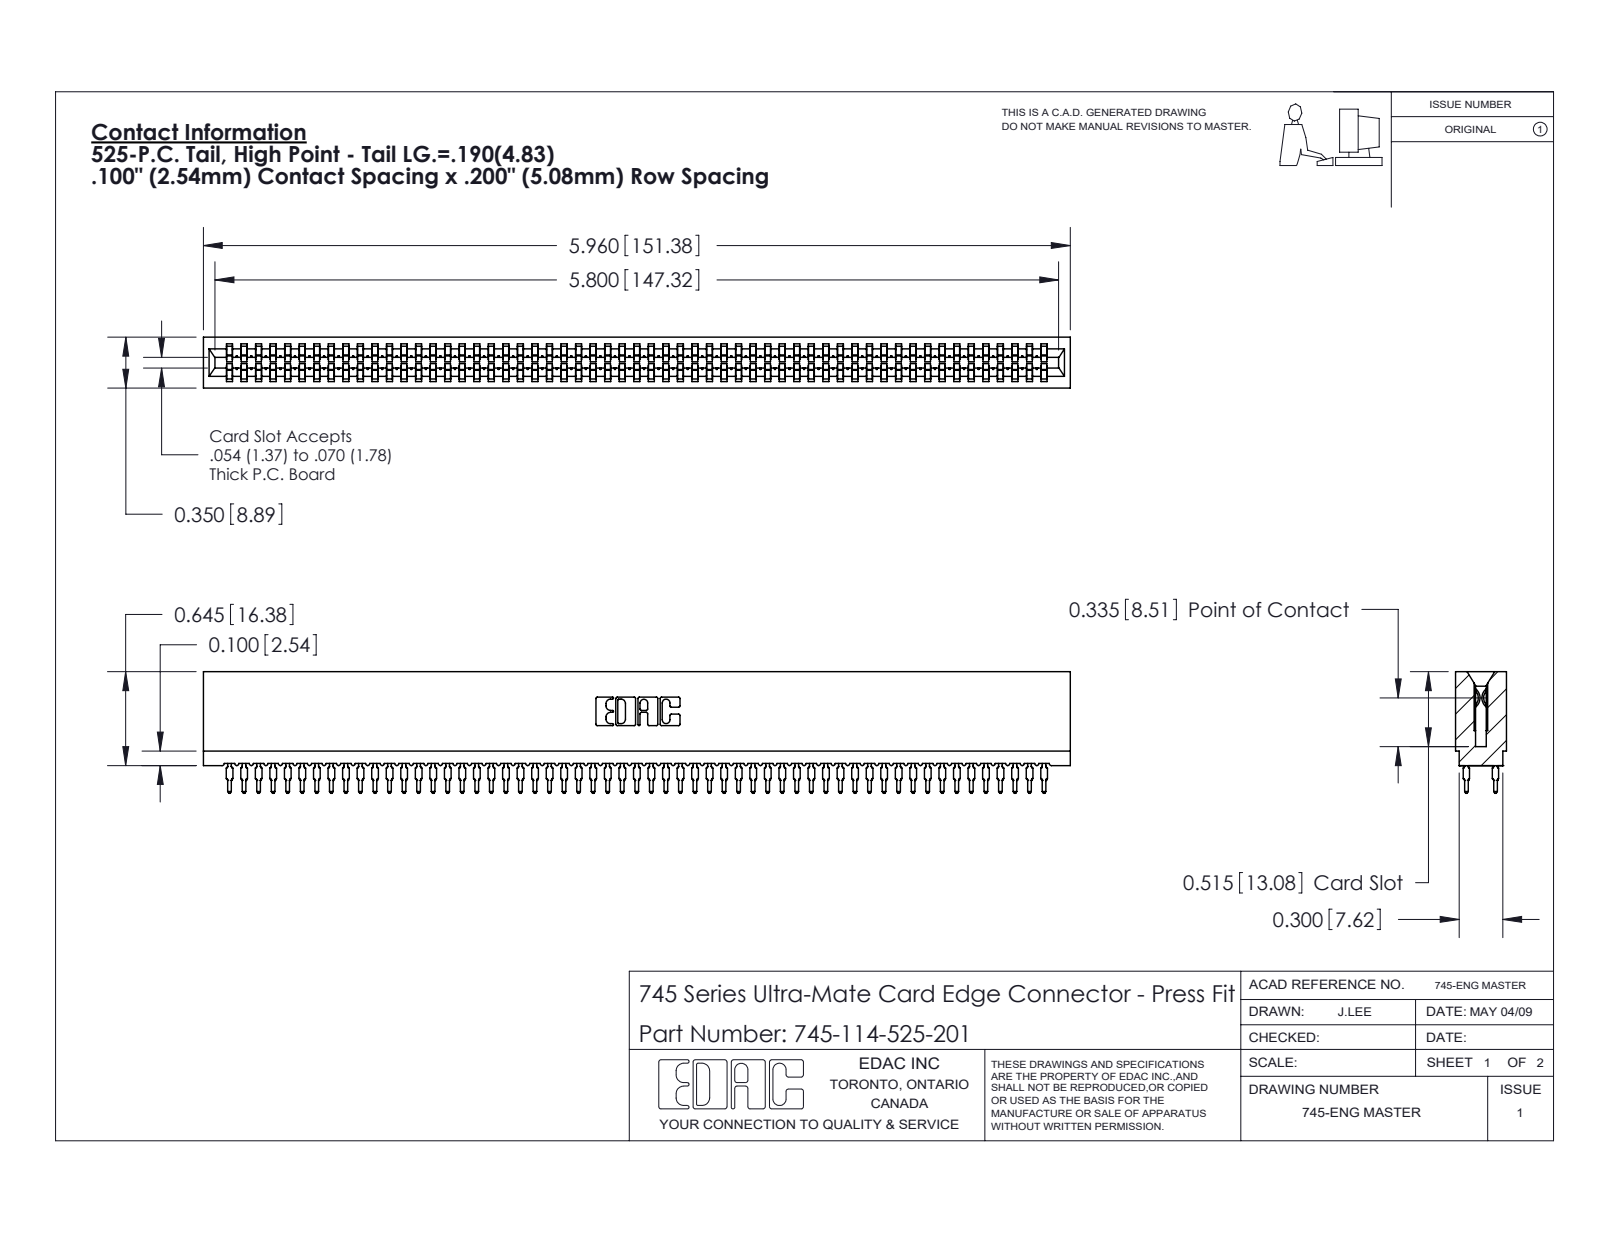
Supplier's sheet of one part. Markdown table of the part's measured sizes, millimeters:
| quantity | value |
| --- | --- |
| part name | 745 Part_Insulator Option - 01; 745-292-001_525; 745-114-525-201 |
| STEP written by | SolidWorks 2020 (CONFIG_CONTROL_DESIGN) |
| units | millimeters |
| bodies | 115 solids, 10298 faces (5299 planar, 2035 cylindrical, 2964 other) |
| overall size | 151.4 × 21.2 × 8.9 |
| volume | 13 500 mm³ |
| surface area | 27 710 mm² |
| partial cylindrical surfaces (radius × count) | 0.5 × 228, 0.4 × 114, 0.3 × 22, 0.1 × 8, 0.3 × 8, 0.2 × 6, 0.8 × 6, 0.7 × 3 |
| main face-to-face distances | 8.9, 1.6, 7.3, 1.1, 7.7, 0.5, 6.2, 3.5, 5.4, 2.4 |
